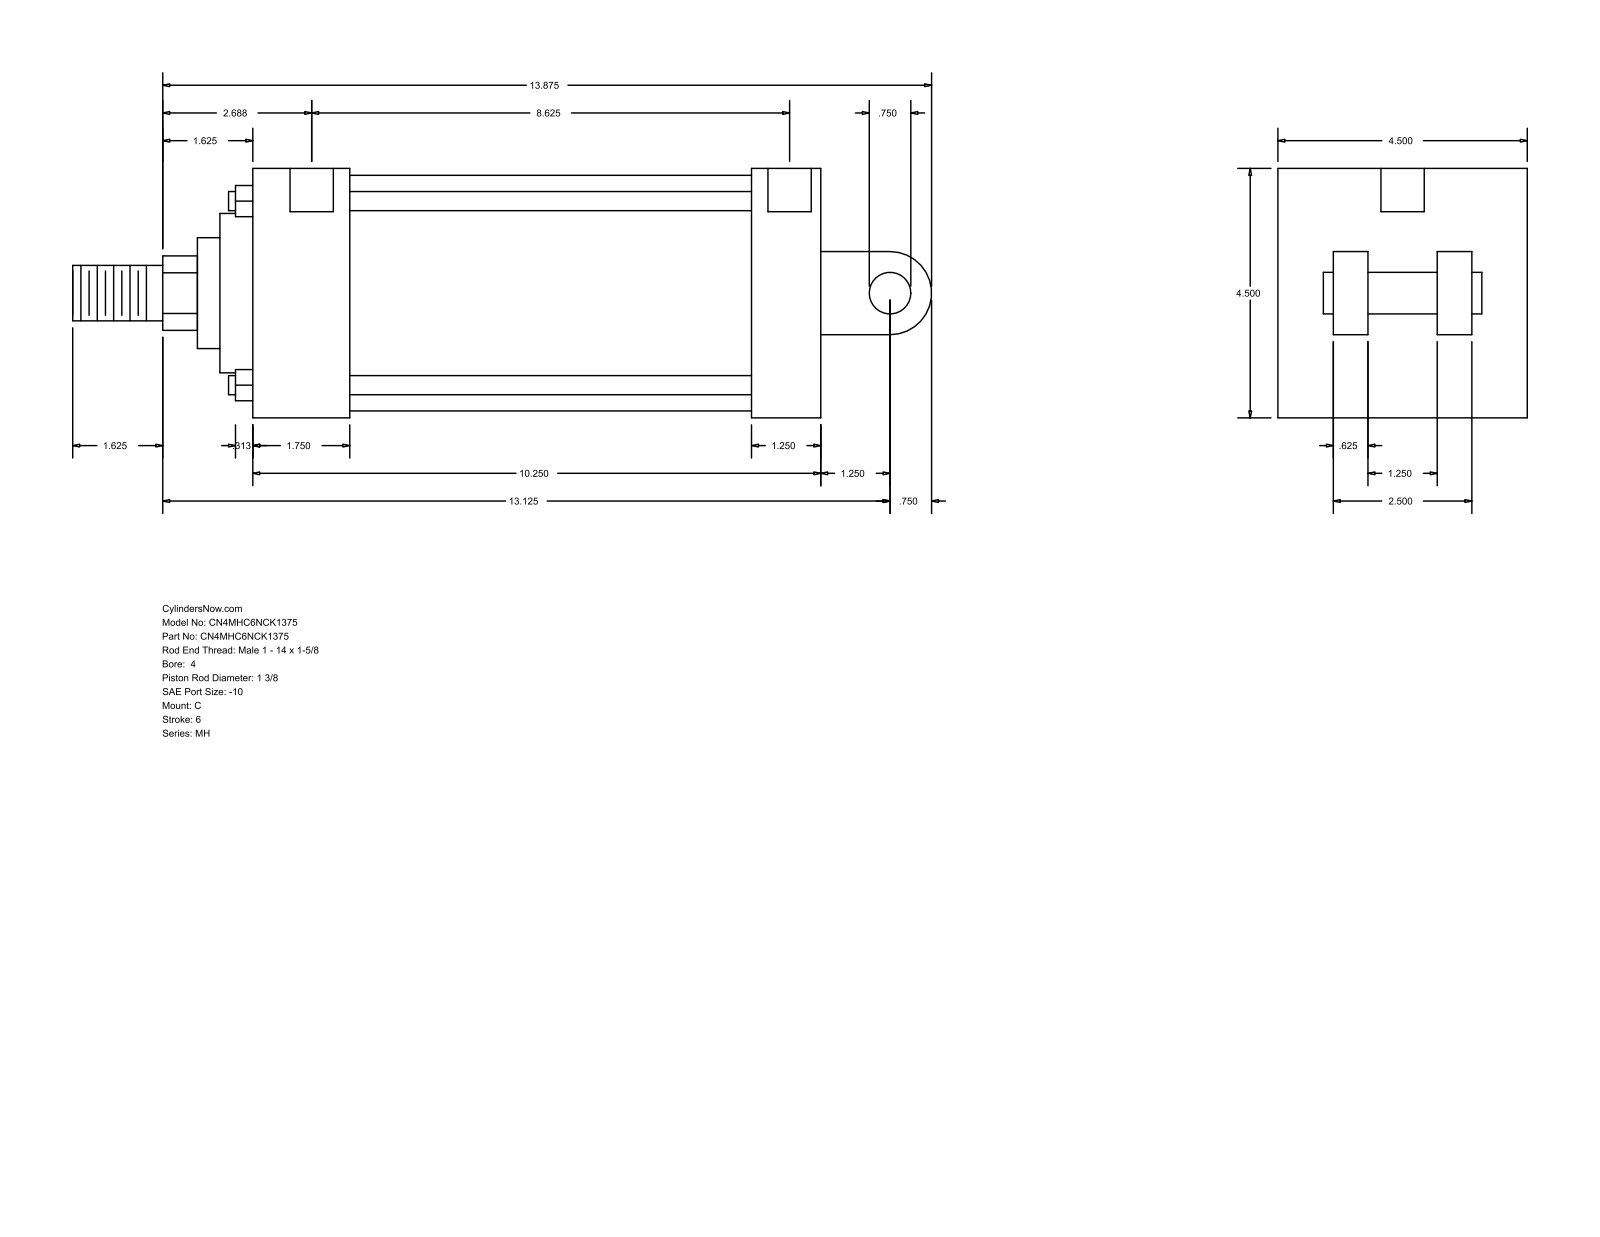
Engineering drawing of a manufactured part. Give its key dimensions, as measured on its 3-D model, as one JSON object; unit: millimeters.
{"part_name": "MH_C__0400_1.375", "step_written_by": "GSSL Pune (CONFIG_CONTROL_DESIGN)", "units": "millimeters", "bodies": {"solids": 0, "faces": 101, "planar": 71, "cylindrical": 30, "other": 0}, "overall_size": [393.7, 114.3, 114.3], "round_holes": [[8.73, 4], [19.84, 2]], "round_bosses_or_shafts": [[8.76, 4], [107.95, 1], [73.03, 1], [50.8, 1], [34.92, 1], [25.4, 1], [19.05, 1]], "partial_cylinders_radius": [[17.06, 1], [19.05, 1]], "face_to_face_distances": [114.3, 260.35, 44.45, 228.61, 184.16, 215.9, 31.74, 41.27, 73.03, 38.1], "hole_center_spacings": [1.59, 220.67, 222.26, 219.08]}
